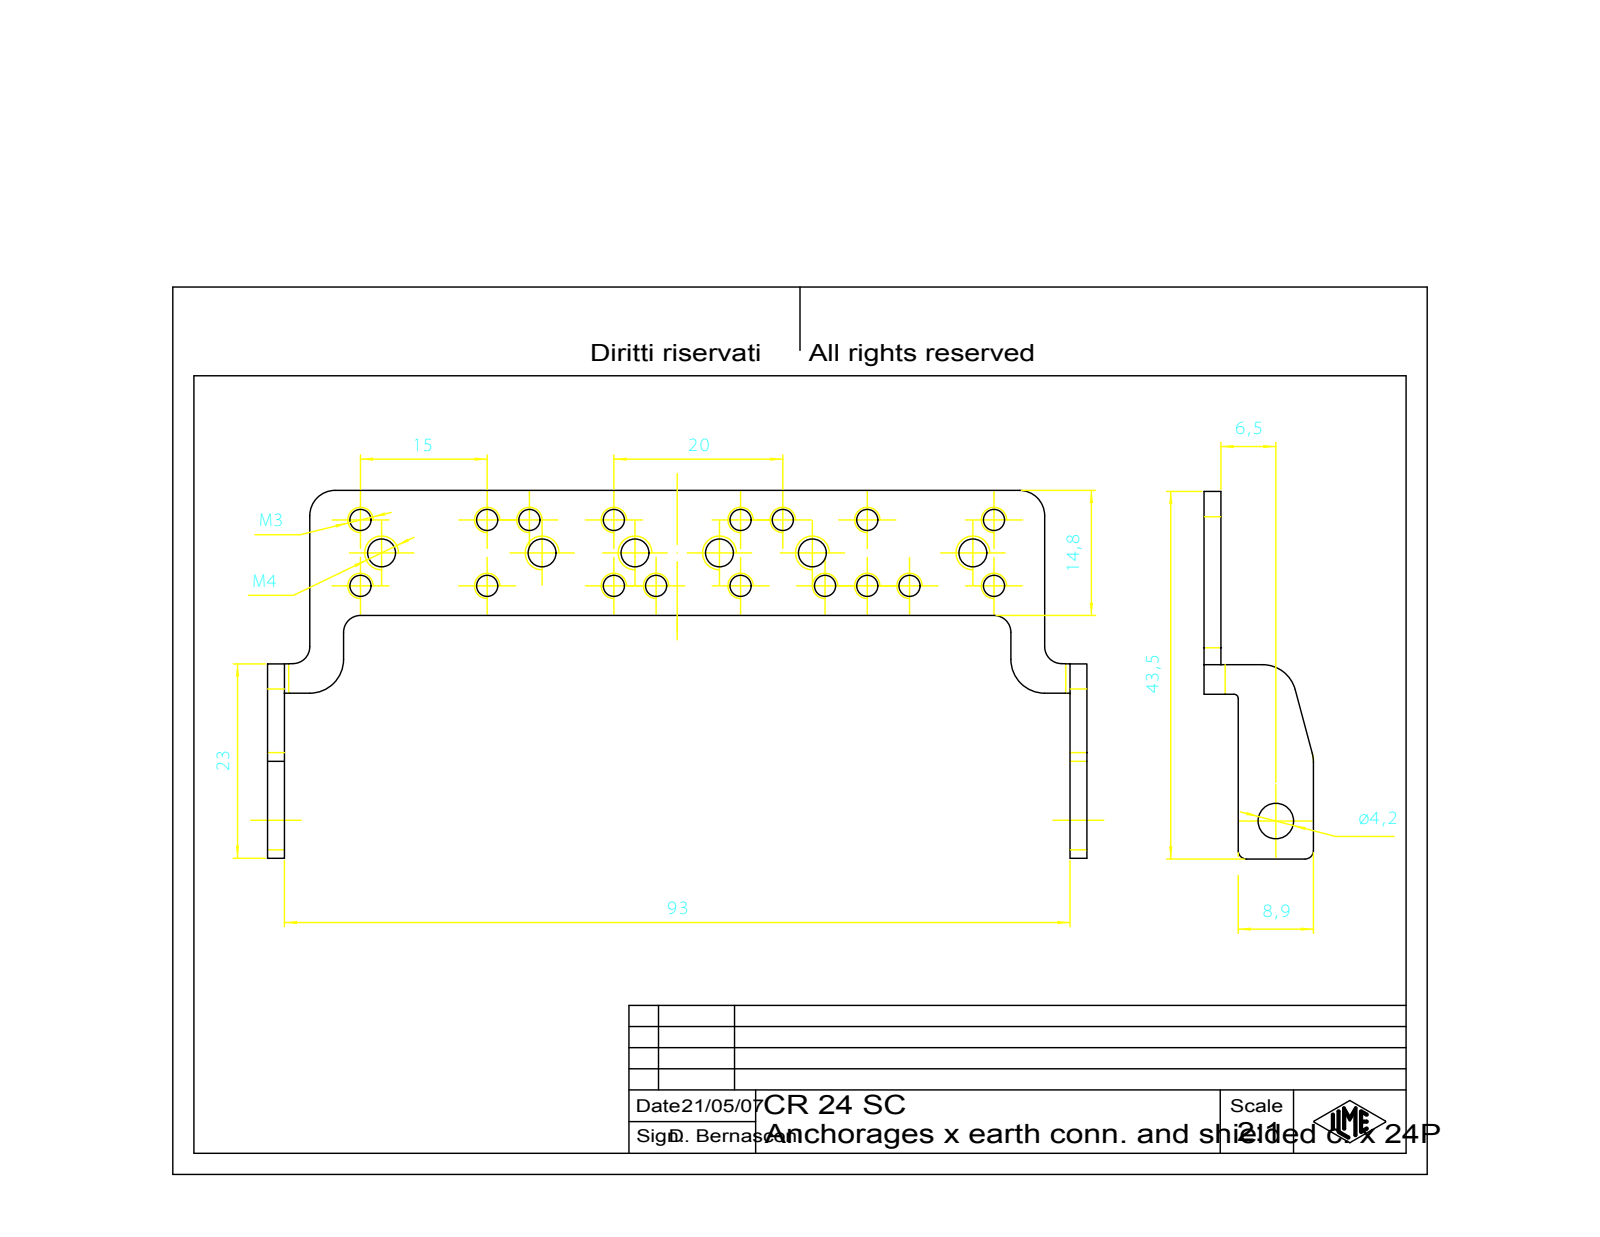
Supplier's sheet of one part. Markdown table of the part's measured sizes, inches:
| quantity | value |
| --- | --- |
| part name | CR_24_SC |
| STEP written by | OneSpace Modeling 15.50B 03-Nov-2007 (C) CoCreate Software GmbH (AUTOMOTIVE_DESIGN) |
| units | inches |
| bodies | 1 solid, 96 faces (24 planar, 72 cylindrical, 0 other) |
| overall size | 3.819 × 1.713 × 0.51 |
| volume | 0.196 in³ |
| surface area | 6.795 in² |
| round holes (diameter × count) | 0.098 × 17, 0.13 × 6, 0.165 × 1 |
| partial cylindrical surfaces (radius × count) | 0.079 × 4, 0.157 × 4, 0.02 × 3, 0.039 × 2, 0.098 × 2, 0.118 × 2 |
| main face-to-face distances | 0.079, 3.74, 3.661, 3.819, 0.583, 0.159, 0.081, 0.197, 3.622, 0.118 |
| hole center spacings | 0.666, 1.181, 0.515, 0.591, 0.182, 1.094, 1.22, 1.68 |
